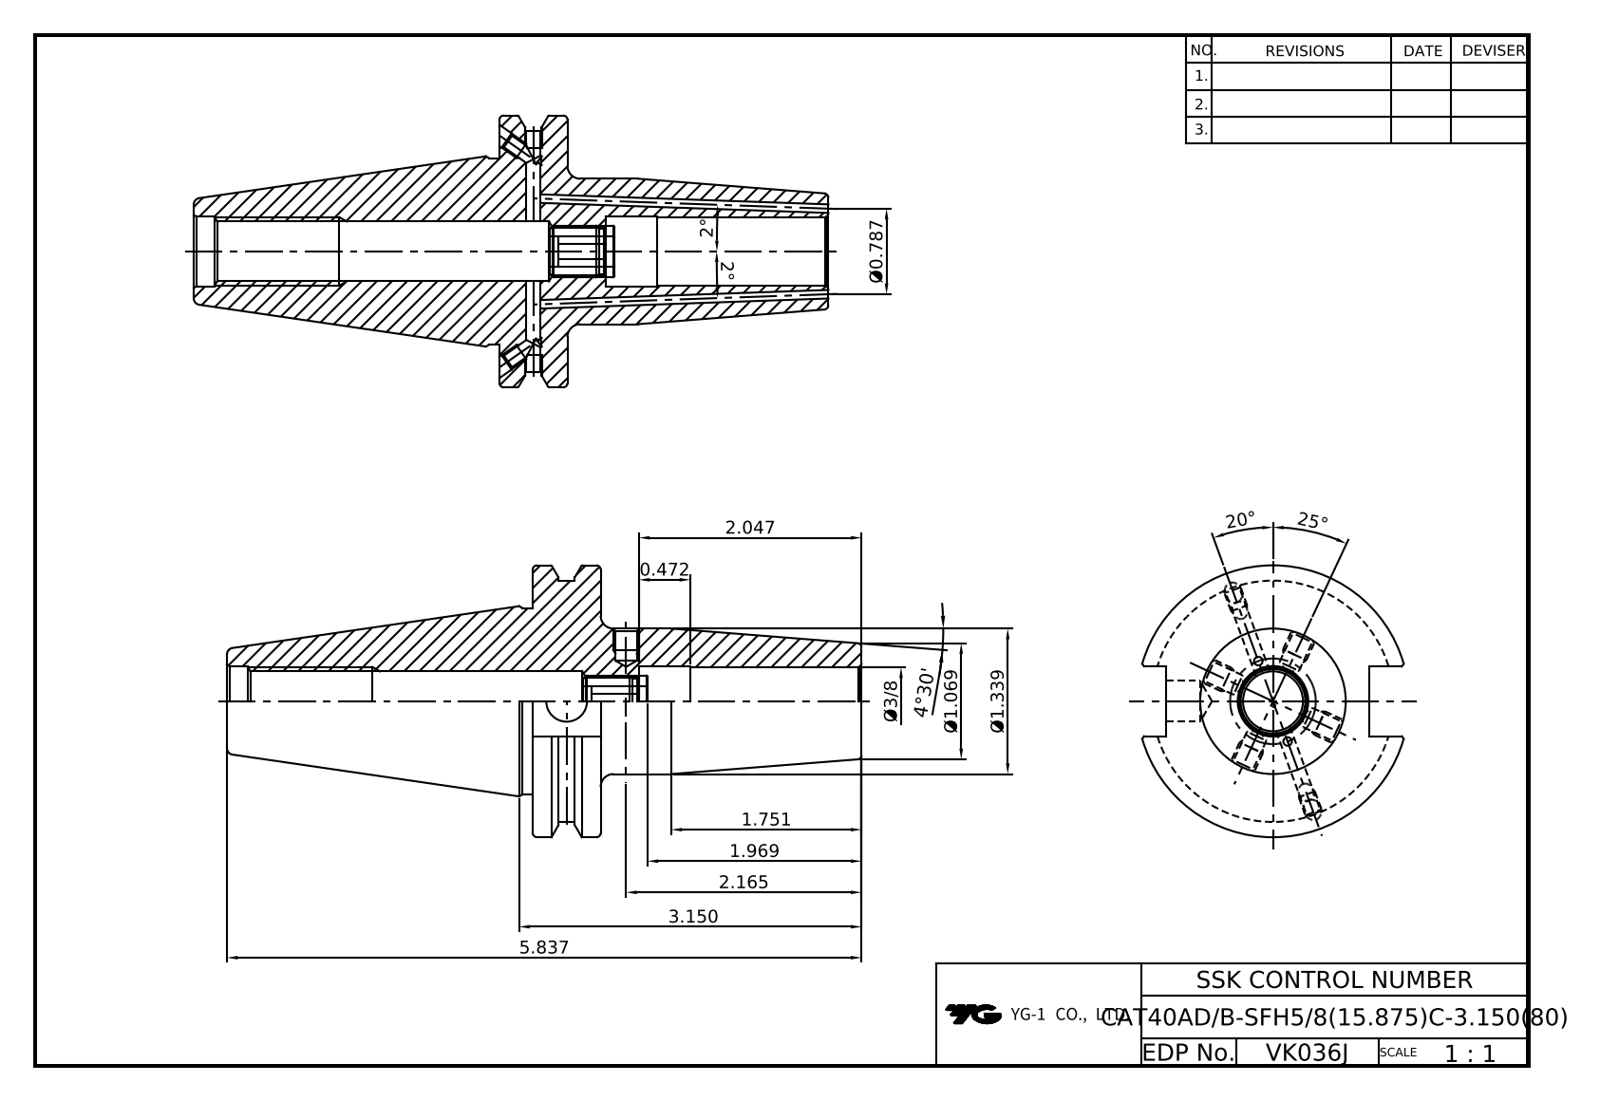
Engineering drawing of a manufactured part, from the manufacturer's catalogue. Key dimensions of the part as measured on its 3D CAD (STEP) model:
Part name (STEP PRODUCT): LO-CAT40ADB-SFH15.875C-80
STEP written by: Autodesk Inventor 2022 (AUTOMOTIVE_DESIGN)
Units: millimetres
Bodies: 1 solid, 91 faces (37 planar, 31 cylindrical, 23 other)
Overall size (bounding box): 148.25 × 63.5 × 61.09
Volume: 136 656 mm³ · Surface area: 30 024 mm²
Round holes (diameter × count): ⌀3.24 ×4, ⌀2.5 ×2, ⌀4 ×2, ⌀4.2 ×2, ⌀9.53 ×1, ⌀10.92 ×1, ⌀13 ×1, ⌀13.39 ×1, ⌀15.88 ×1, ⌀16.3 ×1, ⌀17.07 ×1
Round bosses / shafts (diameter × count): ⌀63.5 ×1, ⌀43.6 ×1, ⌀34 ×1
Partial cylindrical surfaces — rounded edges, fillets, slot ends (radius × count): R28.15 ×1
Main face-to-face distances: 15.88, 76.83, 60.95, 47.6, 16.38, 71.42, 87.3, 148.25, 96.25, 24.83
